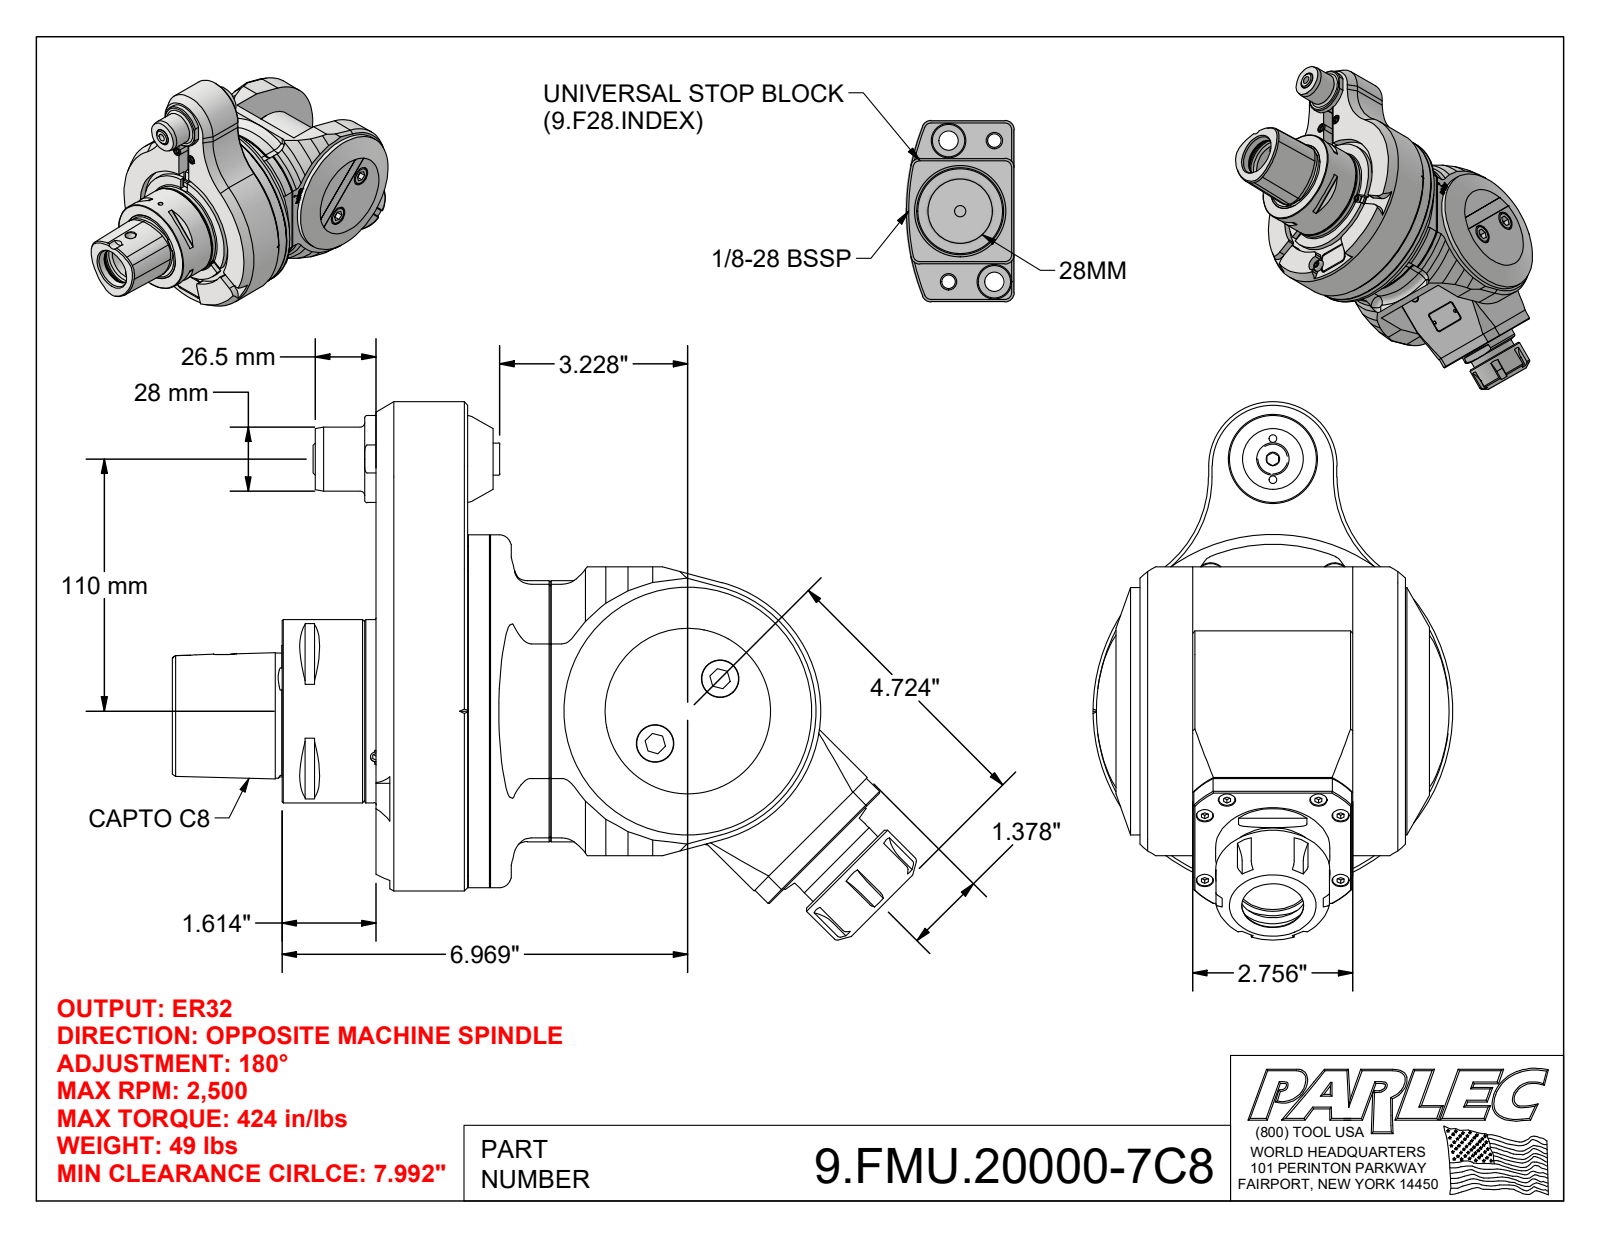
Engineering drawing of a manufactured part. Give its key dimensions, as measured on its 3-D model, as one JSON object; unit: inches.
{"part_name": "9.FMU.20000-7C8; 9_GA3_681_2 (EVO, Type 3, Capto C8, 110mm); 9_FMU_20000", "step_written_by": "Autodesk Inventor 2022 (AUTOMOTIVE_DESIGN)", "units": "inches", "bodies": {"solids": 5, "faces": 920, "planar": 450, "cylindrical": 218, "other": 252}, "overall_size": [12.791, 9.247, 6.181], "volume_in3": 193.8, "surface_area_in2": 580.9, "round_holes": [[0.295, 8], [0.266, 4], [0.331, 4], [0.531, 4], [0.157, 3], [0.165, 3], [0.197, 3], [0.65, 3], [0.126, 2], [0.209, 2], [0.315, 2], [0.335, 2]], "round_bosses_or_shafts": [[0.276, 8], [0.315, 6], [0.512, 4], [0.63, 3], [1.102, 2], [0.098, 2], [6.063, 1], [5.669, 1]], "partial_cylinders_radius": [[0.079, 8], [0.591, 7], [0.118, 6], [0.276, 6], [0.039, 4], [0.197, 4], [0.394, 4], [0.236, 3]], "face_to_face_distances": [0.906, 0.807, 3.661, 3.563, 4.469, 0.197, 1.378, 2.756, 1.181, 2.579], "hole_center_spacings": [1.407, 2.52, 0.537, 1.091, 1.574, 1.99, 1.991, 2.763]}
